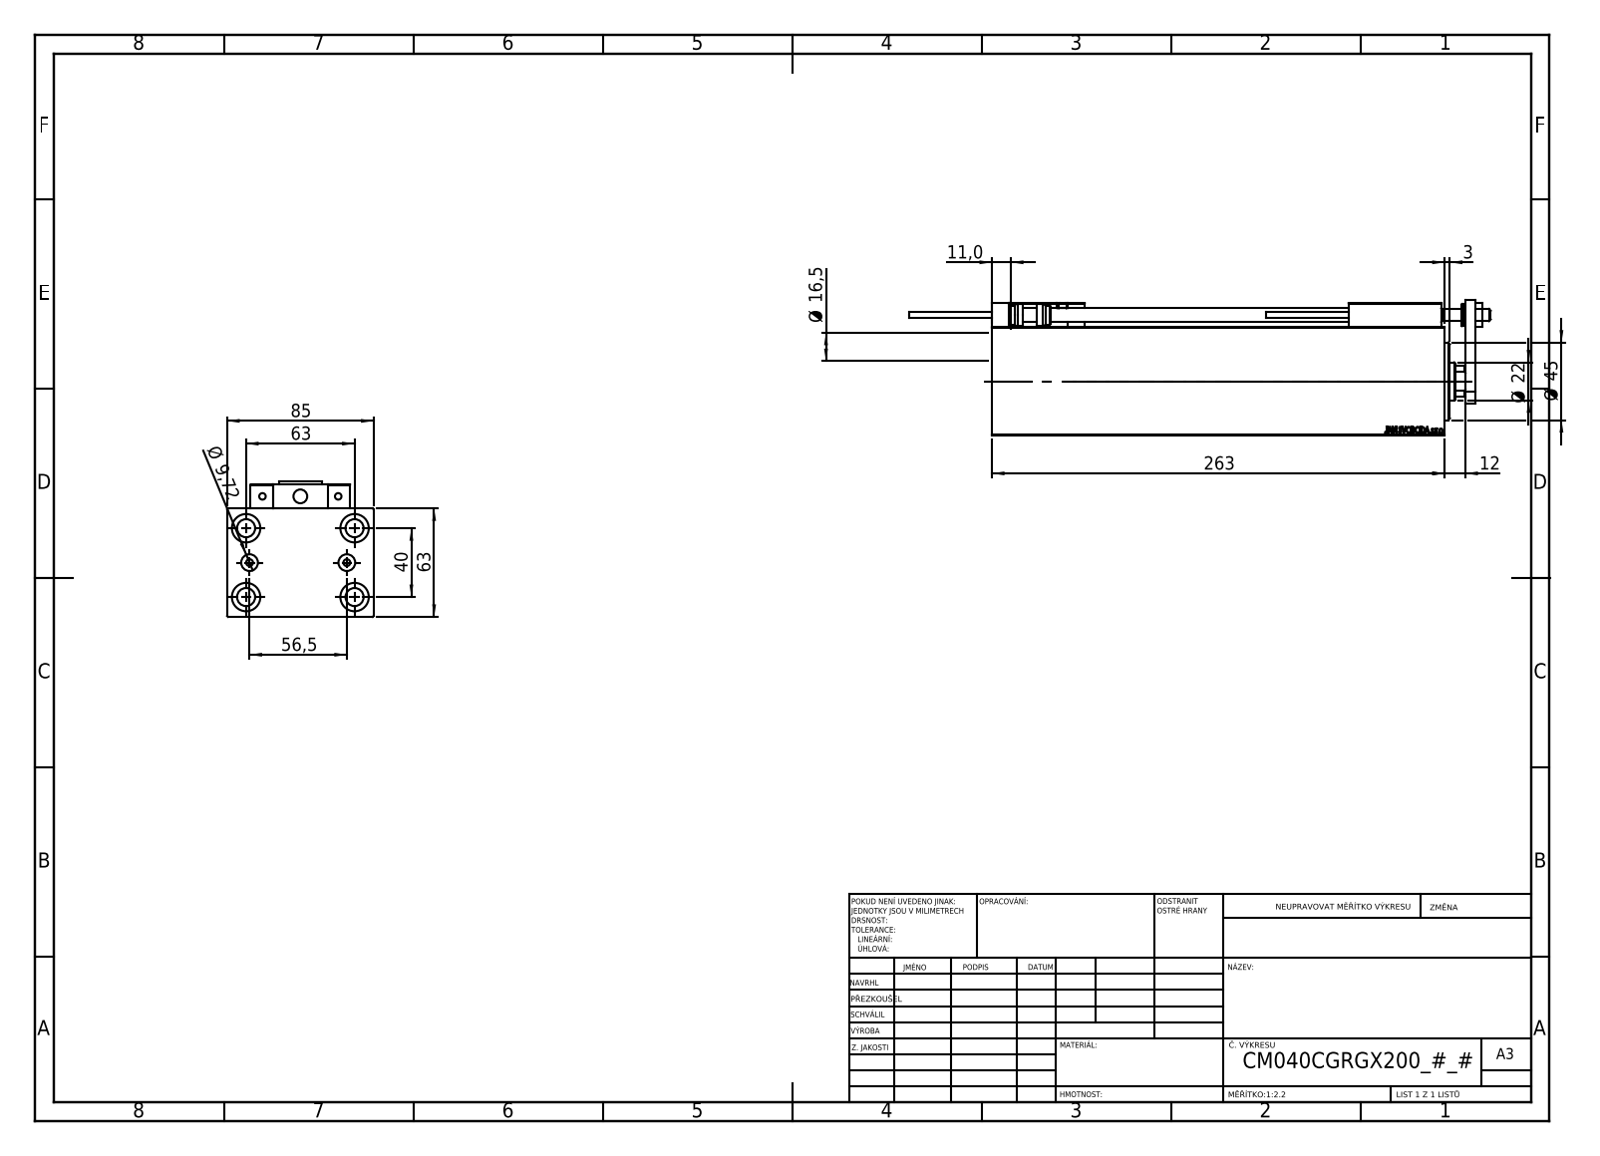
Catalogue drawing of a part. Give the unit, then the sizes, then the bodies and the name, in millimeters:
Units: millimetres
Overall size (bounding box): 337.7 × 85 × 78.5
Round holes (diameter × count): ⌀4 ×6, ⌀8 ×5, ⌀16.5 ×5, ⌀3.2 ×4, ⌀10.5 ×4, ⌀5 ×2, ⌀9.72 ×2, ⌀7 ×1, ⌀12.5 ×1, ⌀22 ×1, ⌀25.5 ×1, ⌀40 ×1
Round bosses / shafts (diameter × count): ⌀5 ×2, ⌀3.8 ×2, ⌀13 ×1, ⌀11 ×1
Partial cylindrical surfaces — rounded edges, fillets, slot ends (radius × count): R0.3 ×30, R3 ×2, R10.5 ×1
Main face-to-face distances: 63, 85, 12, 251, 263, 14, 77, 15, 18, 30
Hole centre spacings: 37.31, 11.37, 20, 20.1, 20.5, 29.59, 29.69, 36.06
Volume: 1 185 000 mm³ · Surface area: 220 594 mm²
Bodies: 23 solids, 1278 faces (560 planar, 184 cylindrical, 534 other)
Part name (STEP PRODUCT): SWITCH DIM B,W; SWITCH_X_FRONT_BACK; SWITCH X; ZARAZKA (+7 more)
STEP written by: SolidWorks 2019 (CONFIG_CONTROL_DESIGN)
